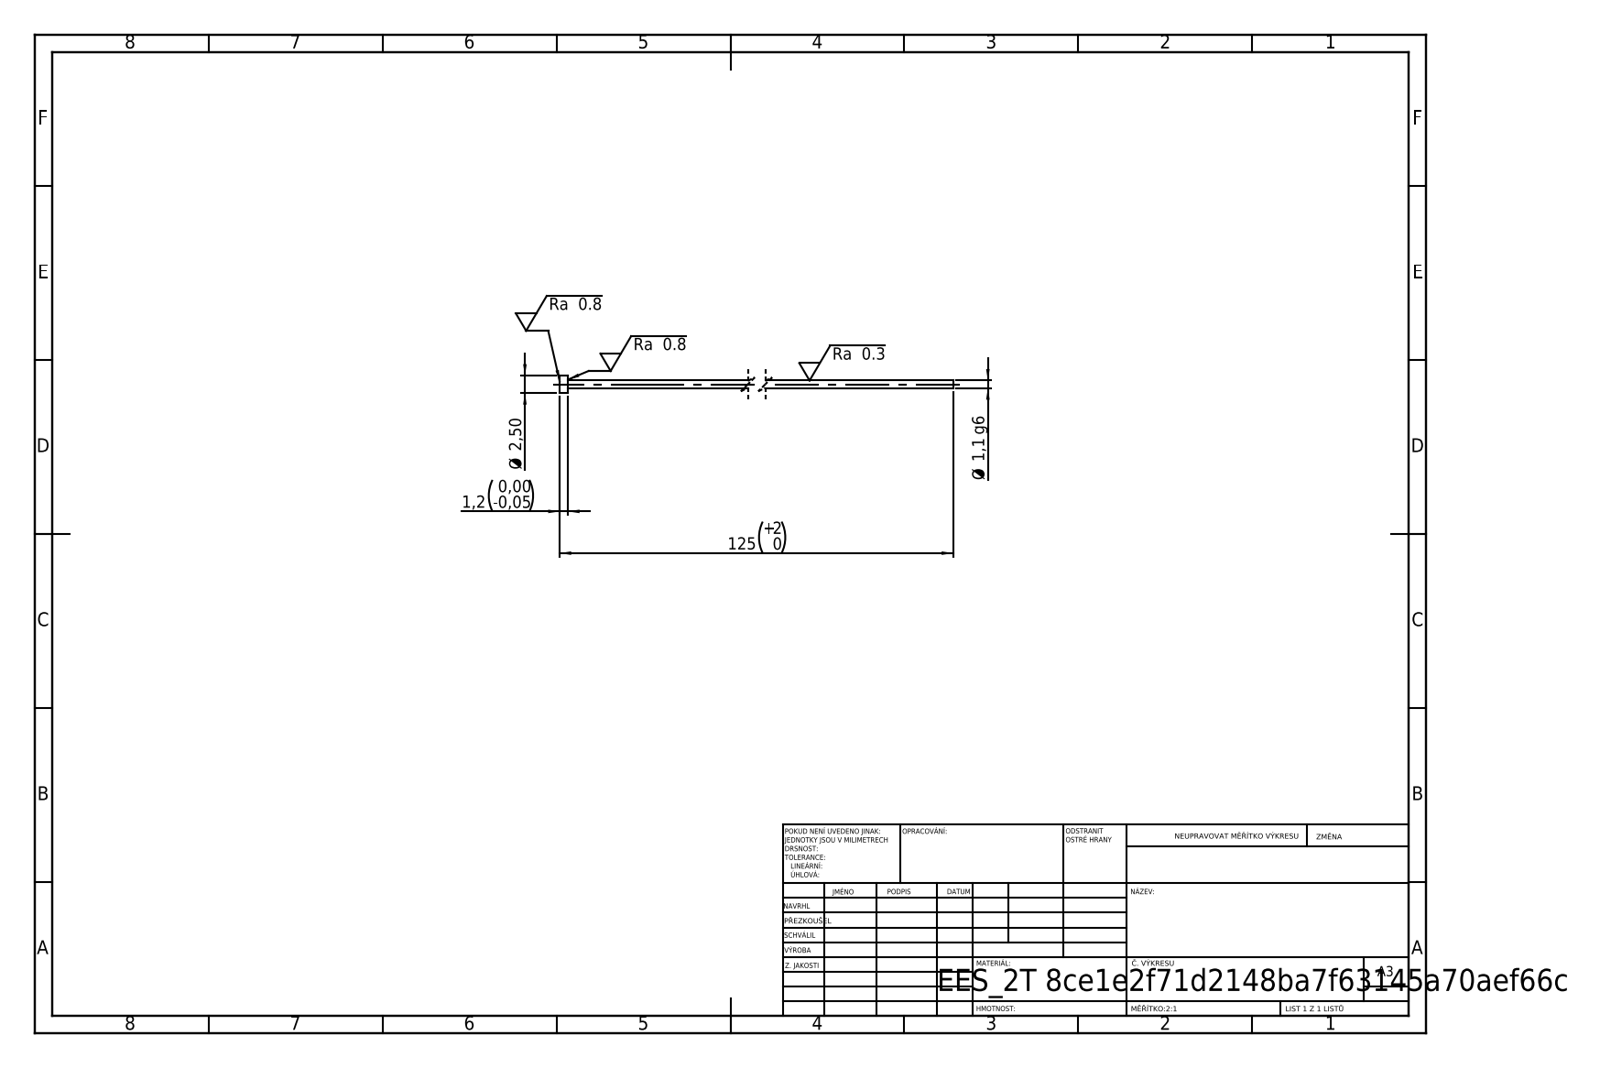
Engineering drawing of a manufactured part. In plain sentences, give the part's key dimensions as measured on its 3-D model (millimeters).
Its 3-D file was written by "SolidWorks 2019 (CONFIG_CONTROL_DESIGN)". It is 1 solid with 7 faces: 3 planar, 4 cylindrical and 0 other. Overall it measures 125 by 2.5 by 2.5 millimeters. Its volume is 124 cubic millimeters and its surface area 447 square millimeters. Round bosses or shafts: 1 of diameter 2.5, 1 of diameter 1.1. The main face-to-face distances are 1.2, 125, 123.8.
